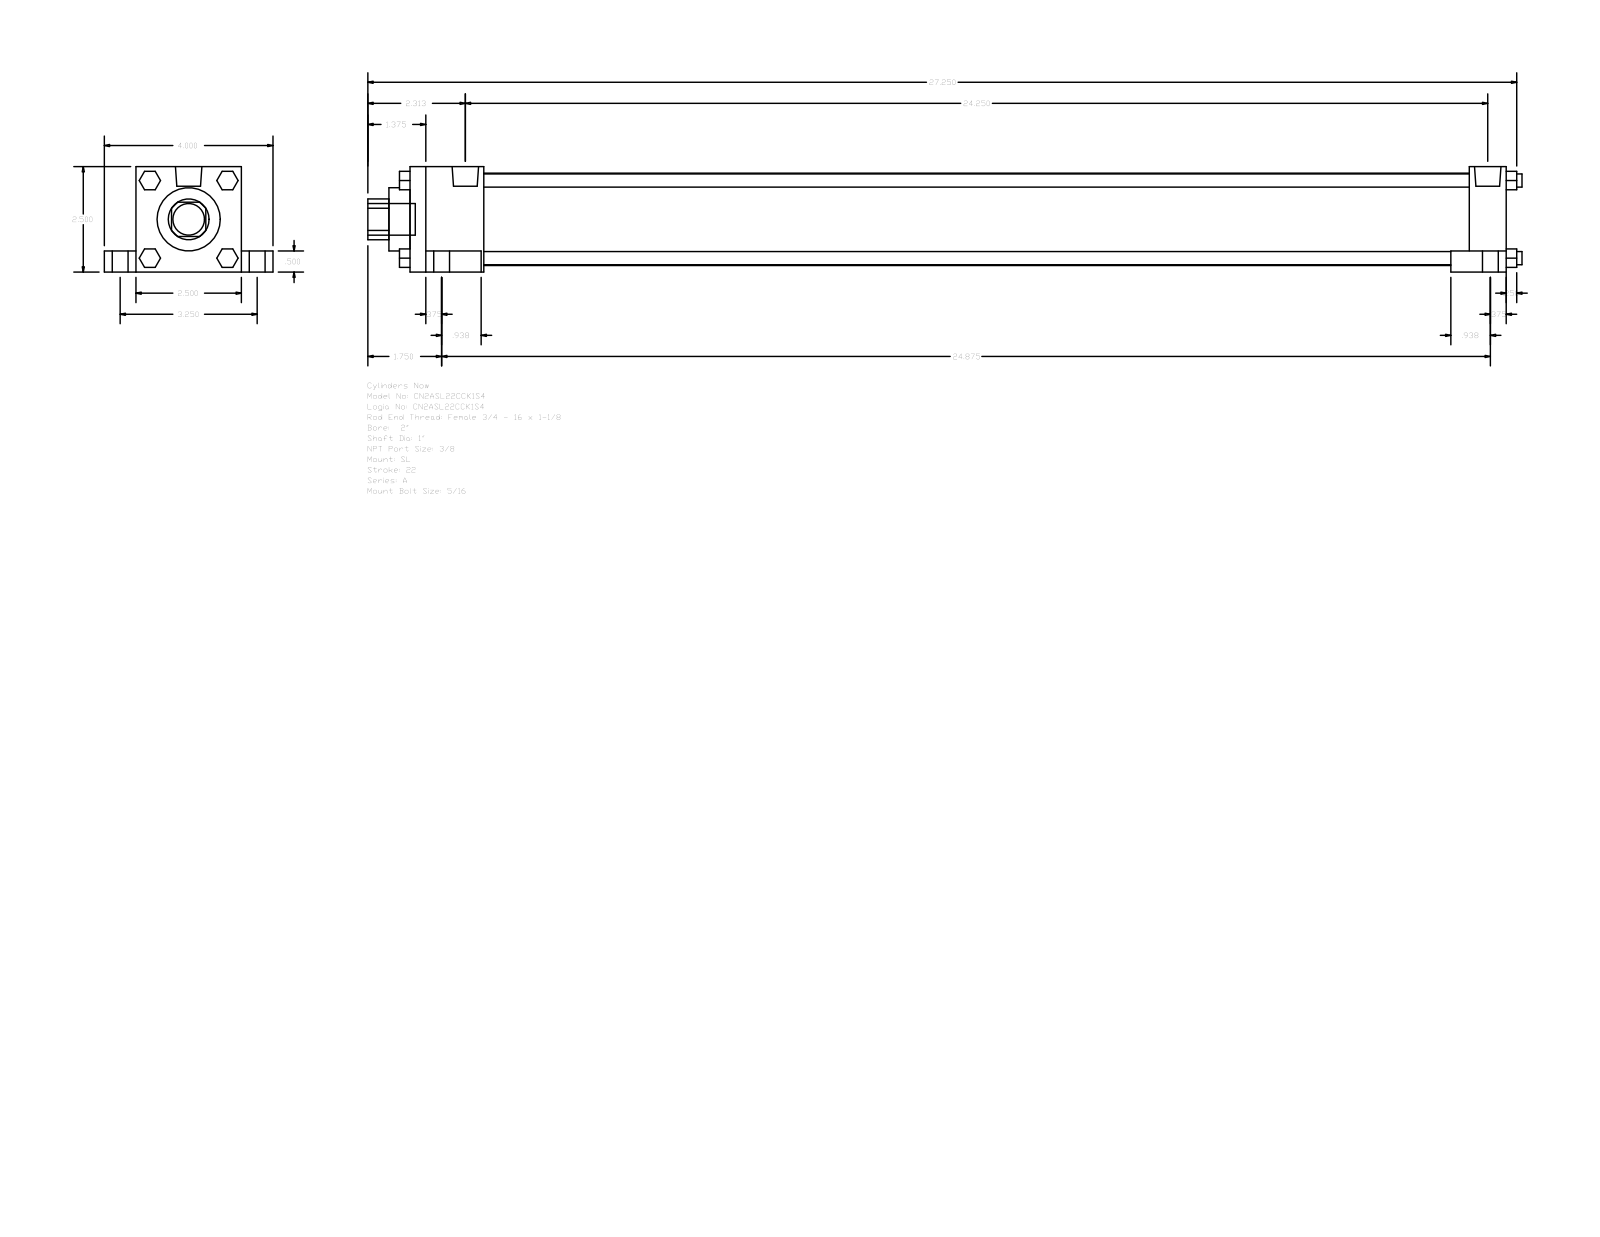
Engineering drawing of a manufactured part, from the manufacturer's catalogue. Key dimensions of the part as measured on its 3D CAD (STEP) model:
Part name (STEP PRODUCT): A_SL__0200_1
STEP written by: GSSL Pune (CONFIG_CONTROL_DESIGN)
Units: millimetres
Bodies: 0 solids, 148 faces (112 planar, 36 cylindrical, 0 other)
Overall size (bounding box): 695.33 × 101.6 × 63.5
Round holes (diameter × count): ⌀25.4 ×1, ⌀38.1 ×1, ⌀55.63 ×1
Round bosses / shafts (diameter × count): ⌀15.88 ×4, ⌀9.53 ×4, ⌀7.94 ×4, ⌀5.56 ×4, ⌀15.93 ×2, ⌀19.05 ×1
Partial cylindrical surfaces — rounded edges, fillets, slot ends (radius × count): R12.29 ×1
Main face-to-face distances: 63.5, 12.7, 660.4, 50.8, 22.22, 19.05, 82.55, 44.45, 615.95, 638.18
